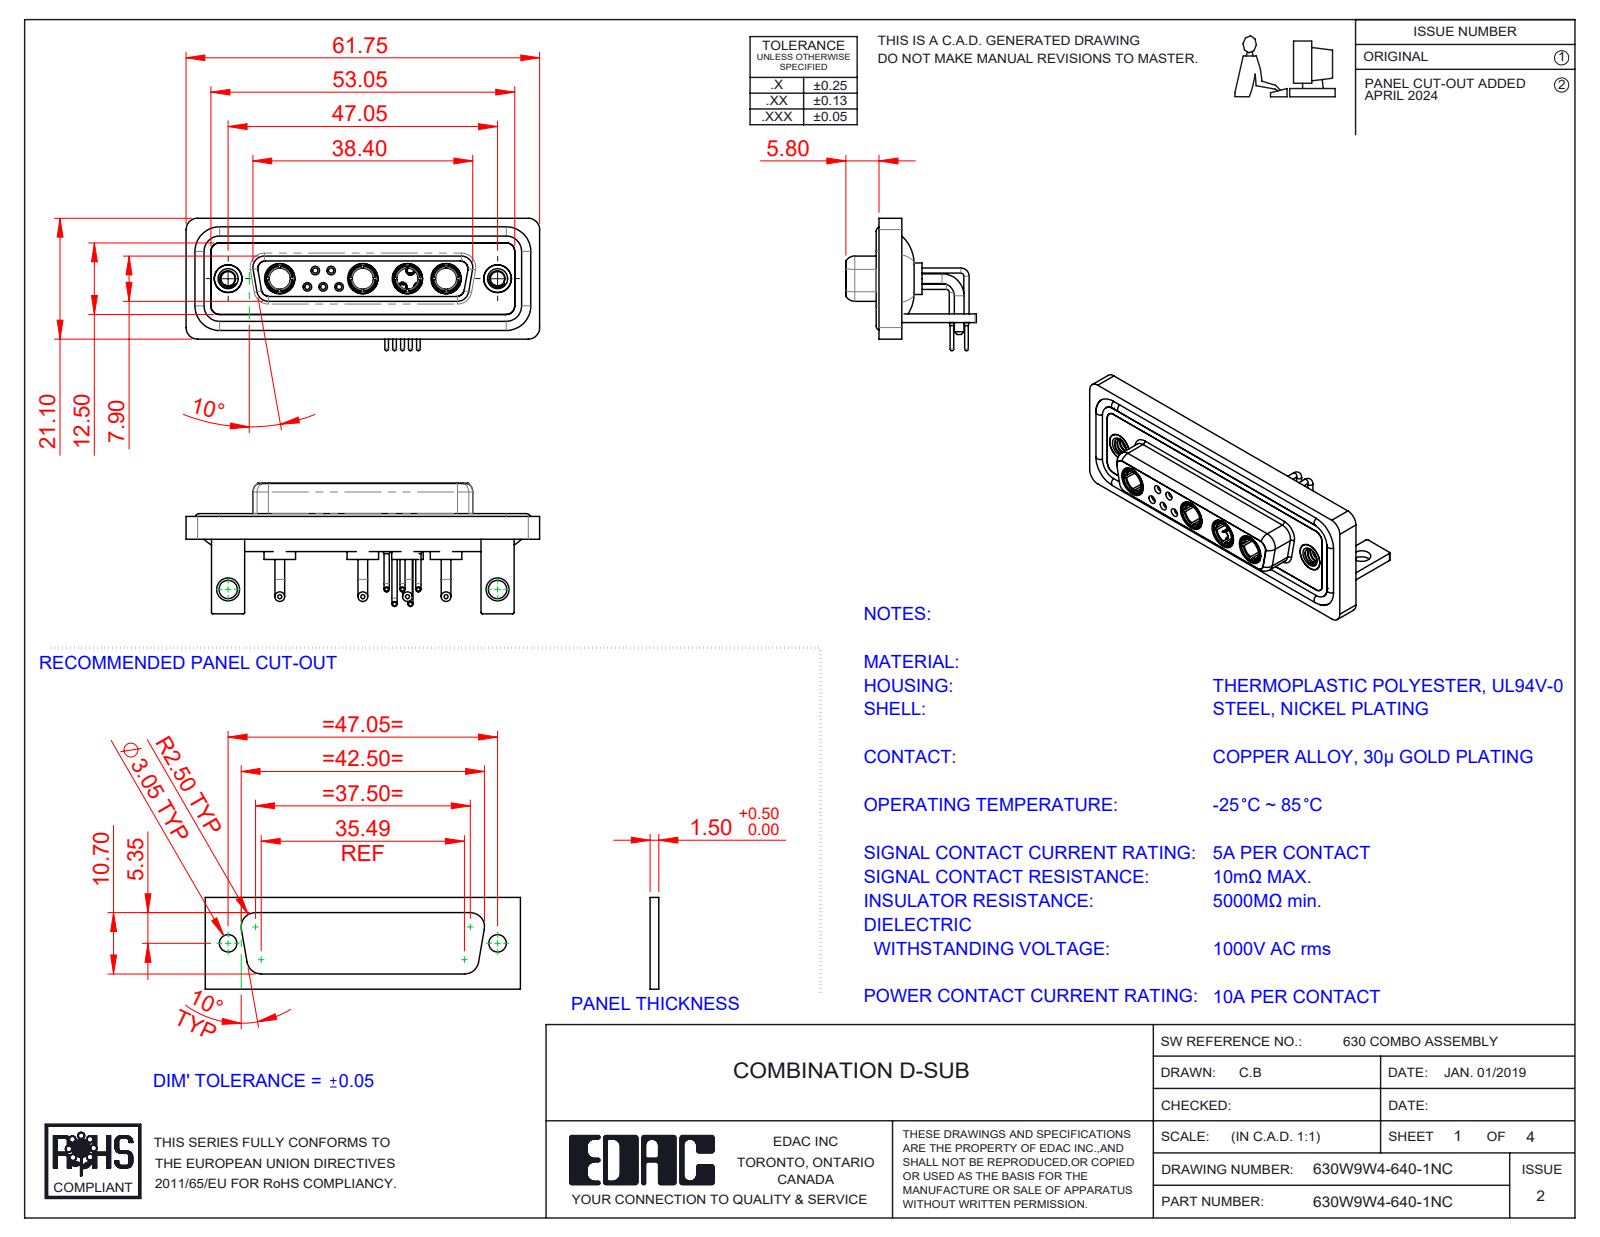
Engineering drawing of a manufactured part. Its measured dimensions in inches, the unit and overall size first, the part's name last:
Units: inches
Overall size (bounding box): 2.431 × 0.91 × 0.898
Round holes (diameter × count): ⌀0.191 ×6, ⌀0.035 ×5, ⌀0.043 ×5, ⌀0.059 ×5, ⌀0.079 ×5, ⌀0.146 ×4, ⌀0.209 ×4, ⌀0.063 ×3, ⌀0.067 ×2, ⌀0.098 ×2, ⌀0.126 ×2, ⌀0.157 ×2
Round bosses / shafts (diameter × count): ⌀0.035 ×10, ⌀0.063 ×9, ⌀0.067 ×8, ⌀0.079 ×5, ⌀0.059 ×5, ⌀0.026 ×5, ⌀0.217 ×4, ⌀0.205 ×4
Partial cylindrical surfaces — rounded edges, fillets, slot ends (radius × count): R0.079 ×19, R0.059 ×18, R0.01 ×16, R0.053 ×8, R0.063 ×8, R0.02 ×5, R0.024 ×4, R0.026 ×4
Main face-to-face distances: 0.016, 0.071, 0.114, 0.146, 0.059, 0.161, 0.043, 0.055, 0.063, 0.098
Hole centre spacings: 0.124, 0.109, 0.198, 0.545, 0.436, 0.504, 0.61, 0.218
Volume: 0.524 in³ · Surface area: 22.6 in²
Bodies: 22 solids, 1005 faces (316 planar, 425 cylindrical, 264 other)
Part name (STEP PRODUCT): 630Combo Shell Front_25 Contacts; 630Combo Stabilizer Bracket_50 Contacts; 630Combo Contact Row 2_50 Contacts; 630Combo Waterproof Housing_25 Contacts (+6 more)
STEP written by: SolidWorks 2023 (CONFIG_CONTROL_DESIGN)
